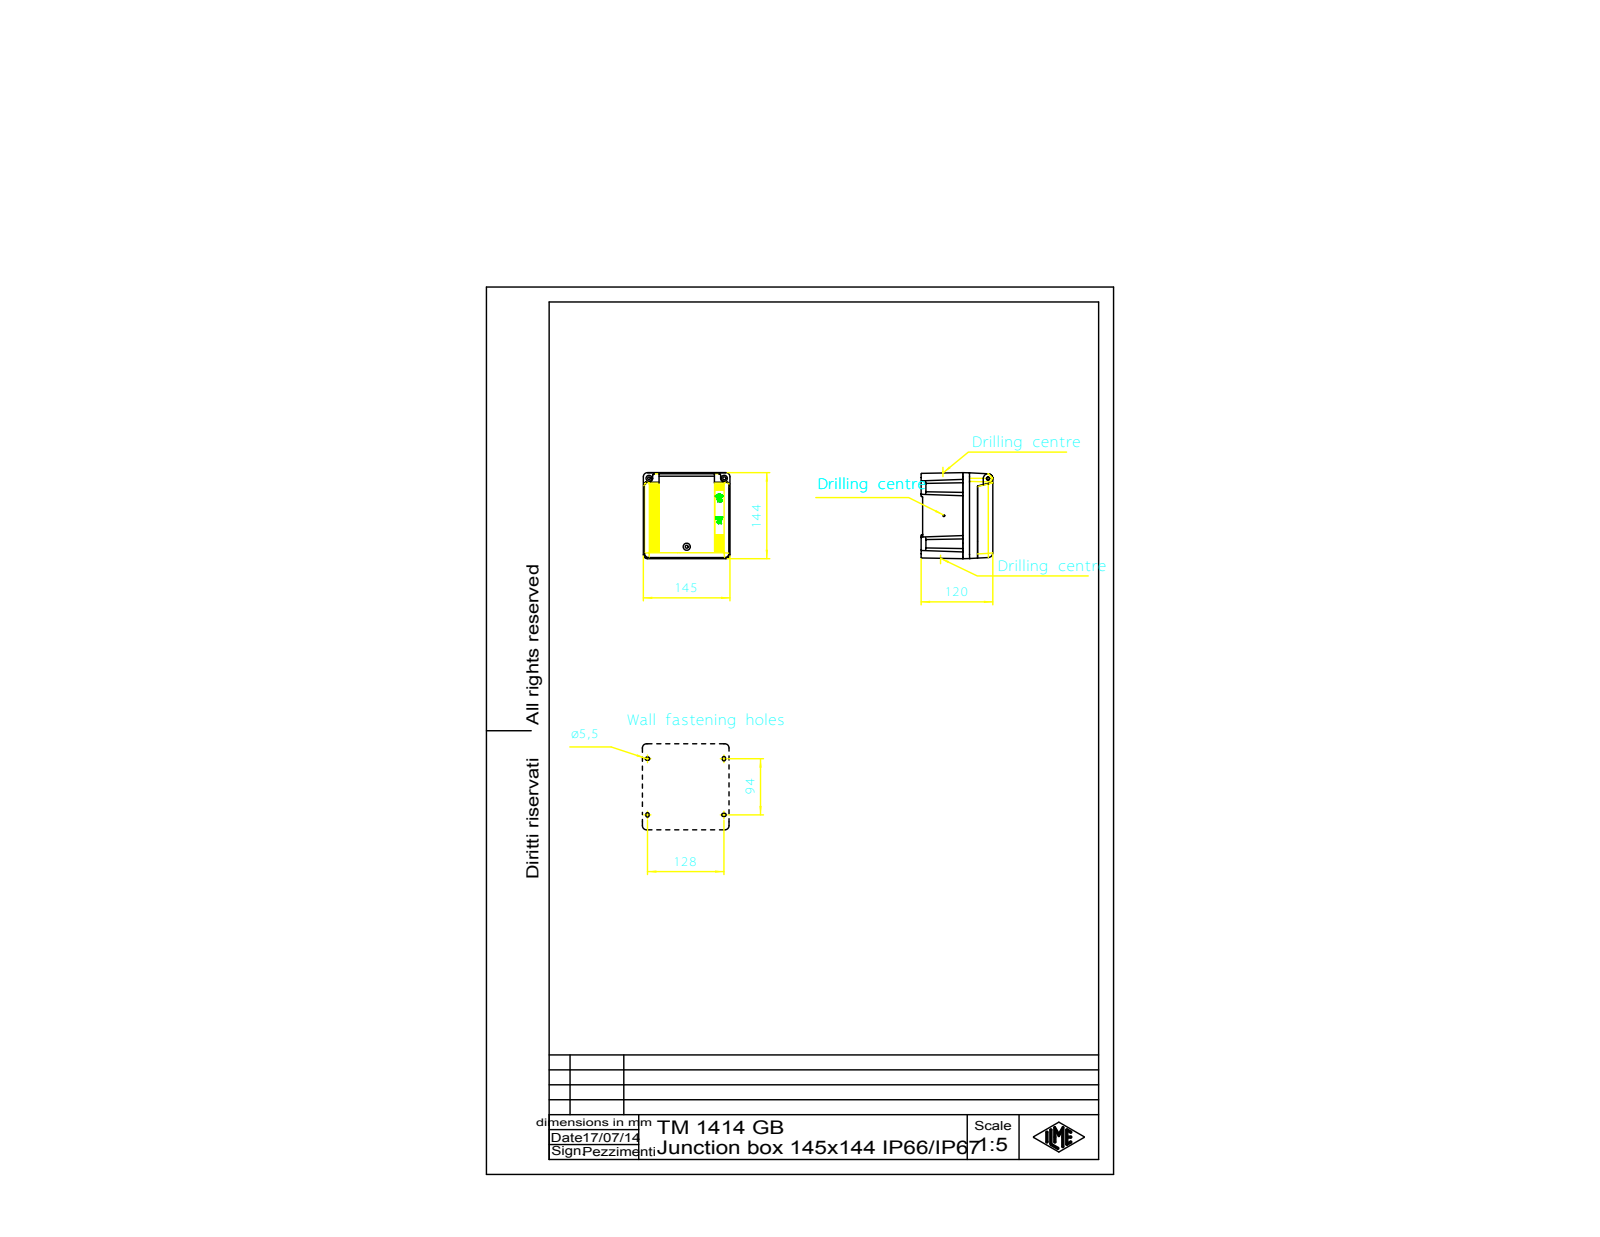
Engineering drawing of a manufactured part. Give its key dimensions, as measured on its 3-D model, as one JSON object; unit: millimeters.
{"part_name": "CALOTTA_1414; SCATOLA_1414; SPORTELLO_1414; TM_1414_GB", "step_written_by": "Creo Elements/Direct Modeling 20.5B 27-May-2023 (C) Parametric Technology GmbH (AUTOMOTIVE_DESIGN)", "units": "millimeters", "bodies": {"solids": 3, "faces": 1218, "planar": 939, "cylindrical": 166, "other": 113}, "overall_size": [145, 144, 120.4], "volume_mm3": 883019, "surface_area_mm2": 257671, "round_holes": [[5.2, 4], [4.5, 2], [5, 1], [5.4, 1]], "round_bosses_or_shafts": [[8.5, 5], [5, 5], [6.7, 2], [4, 2]], "partial_cylinders_radius": [[3.5, 16], [7, 12], [0.25, 11], [2.7, 8], [3, 8], [8, 8], [9.5, 8], [0.5, 5]], "face_to_face_distances": [5, 112.5, 67.5, 45, 92, 87, 117.5, 25.5, 3.99, 72.5], "hole_center_spacings": [68.9, 115.39, 62.13, 63.87, 125, 126, 130.69, 177.49]}
